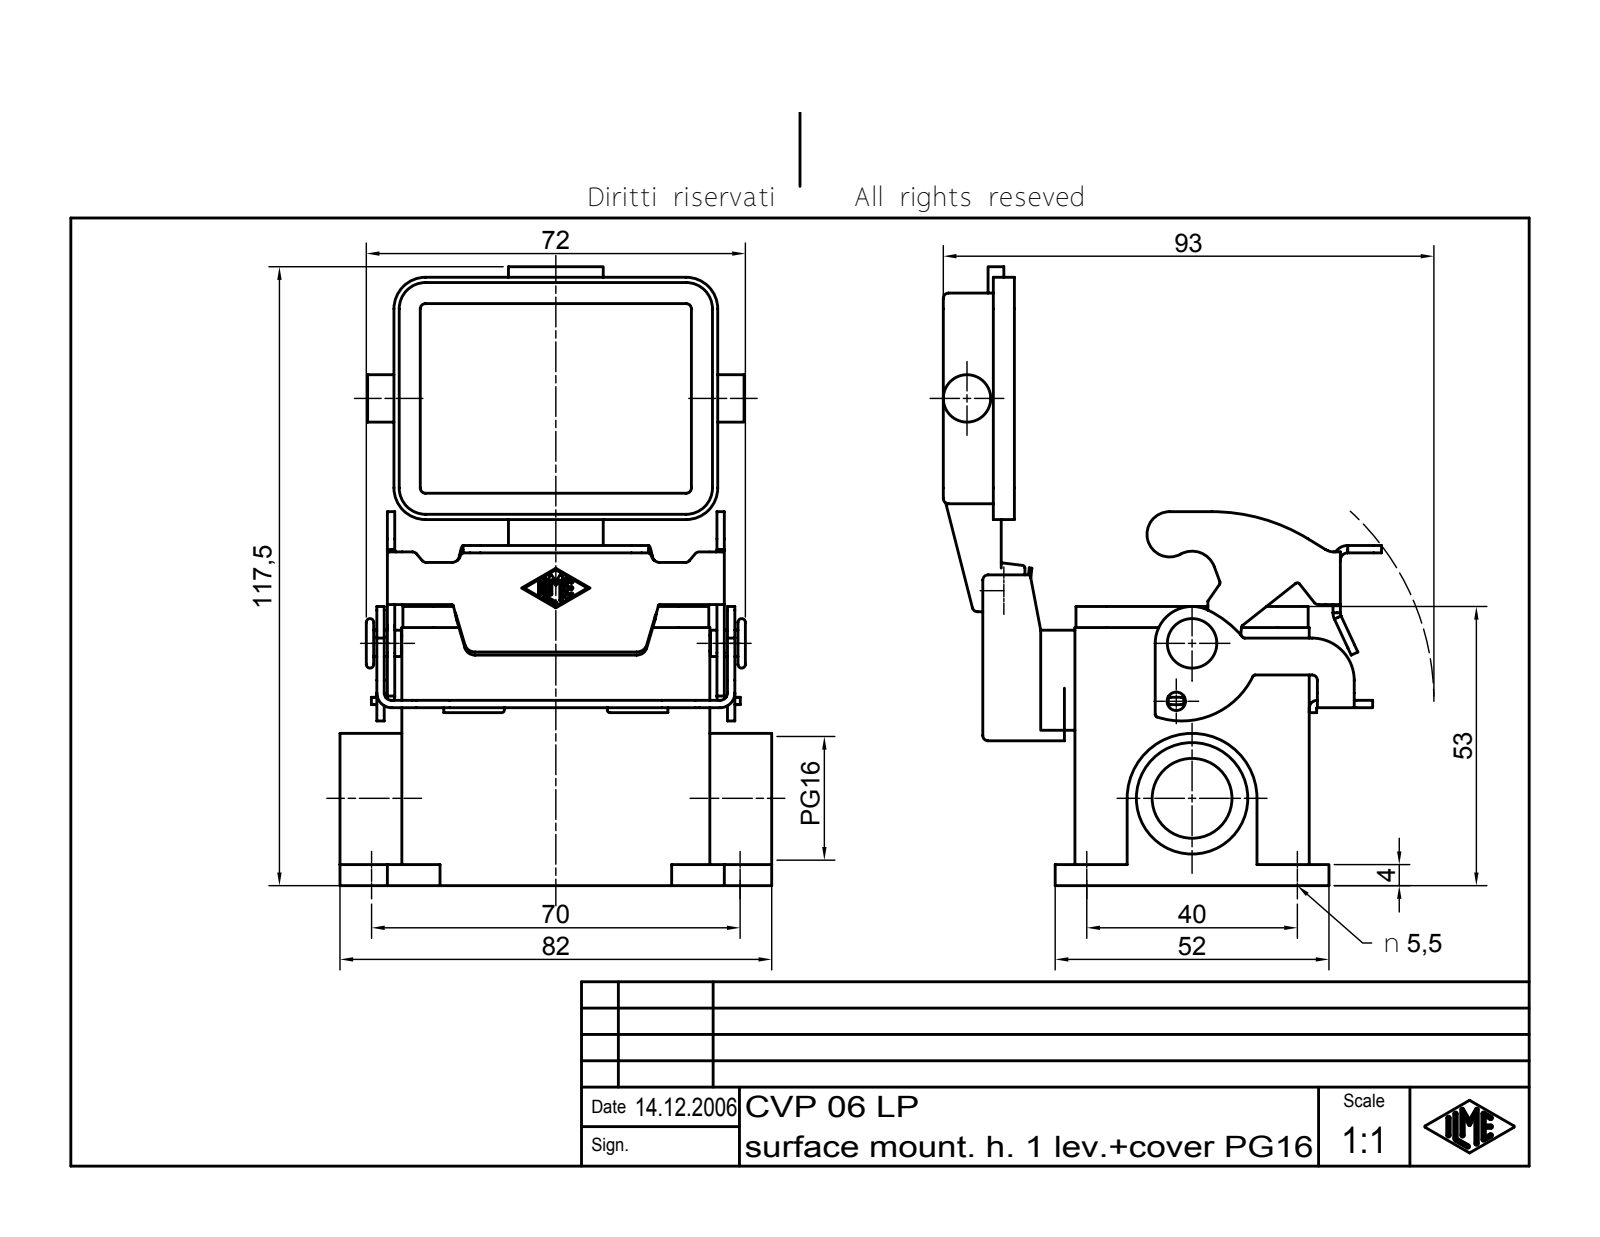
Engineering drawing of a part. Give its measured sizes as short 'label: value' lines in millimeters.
name: CVP 06 LP
written by: Autodesk Inventor 7 (AUTOMOTIVE_DESIGN)
unit: mm
bodies: 4 solids, 590 faces (232 planar, 193 cylindrical, 165 other)
size: 117.5 × 83.23 × 82
volume: 91 566 mm³; area: 55 792 mm²
holes: 4× ⌀5.5, 1× ⌀3.5, 1× ⌀4, 1× ⌀15.16, 1× ⌀21.16
bosses: 2× ⌀5, 1× ⌀9, 1× ⌀7, 1× ⌀3.2, 1× ⌀3
rounds: 32× R1, 15× R0.25, 10× R0.5, 9× R1.5, 8× R6, 7× R2, 6× R1.4, 6× R2.8
face distances: 4, 40.5, 2, 44.5, 69.5, 13.5, 1.5, 23.5, 25, 10.75
hole spacings: 40, 70, 80.62, 18.66
